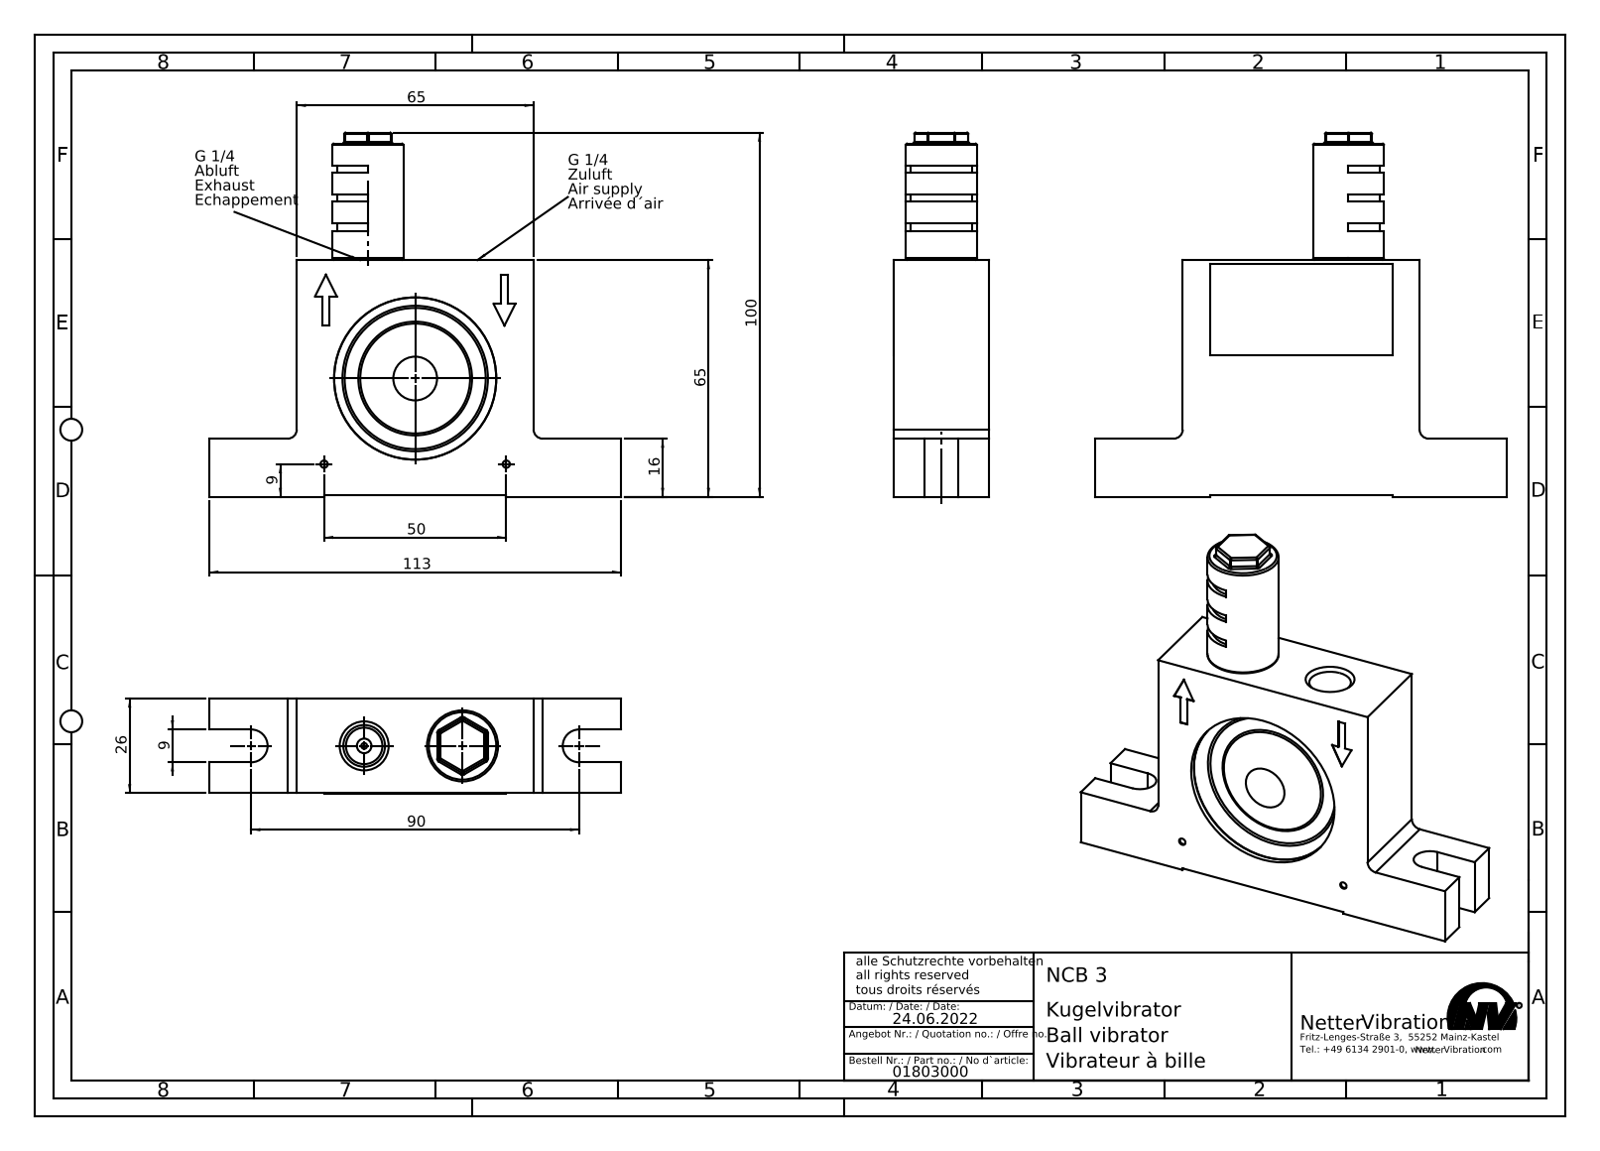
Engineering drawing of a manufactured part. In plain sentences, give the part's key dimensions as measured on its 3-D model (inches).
The part is named "NCB 3 Kugelvibrator #01803000". Its 3-D file was written by "SolidWorks 2015 (AUTOMOTIVE_DESIGN)". It is 3 solids with 220 faces: 102 planar, 49 cylindrical and 69 other. Overall it measures 4.449 by 3.937 by 1.024 inches. Its volume is 7.51 cubic inches and its surface area 44.36 square inches. Round holes: 2 of diameter 0.079, 2 of diameter 0.394, 2 of diameter 0.451, 1 of diameter 1.654, 1 of diameter 1.752. Round bosses or shafts: 1 of diameter 0.768, 1 of diameter 0.518. Partial cylindrical surfaces (rounded edges, fillets, slot ends): 18 of radius 0.02, 2 of radius 0.098, 2 of radius 0.177, 1 of radius 0.335. The main face-to-face distances are 1.024, 2.559, 0.748, 0.276, 0.02, 2.539, 0.63, 1.929, 0.61, 0.335. The hole center spacings are 1.351, 1.063, 1.969.
